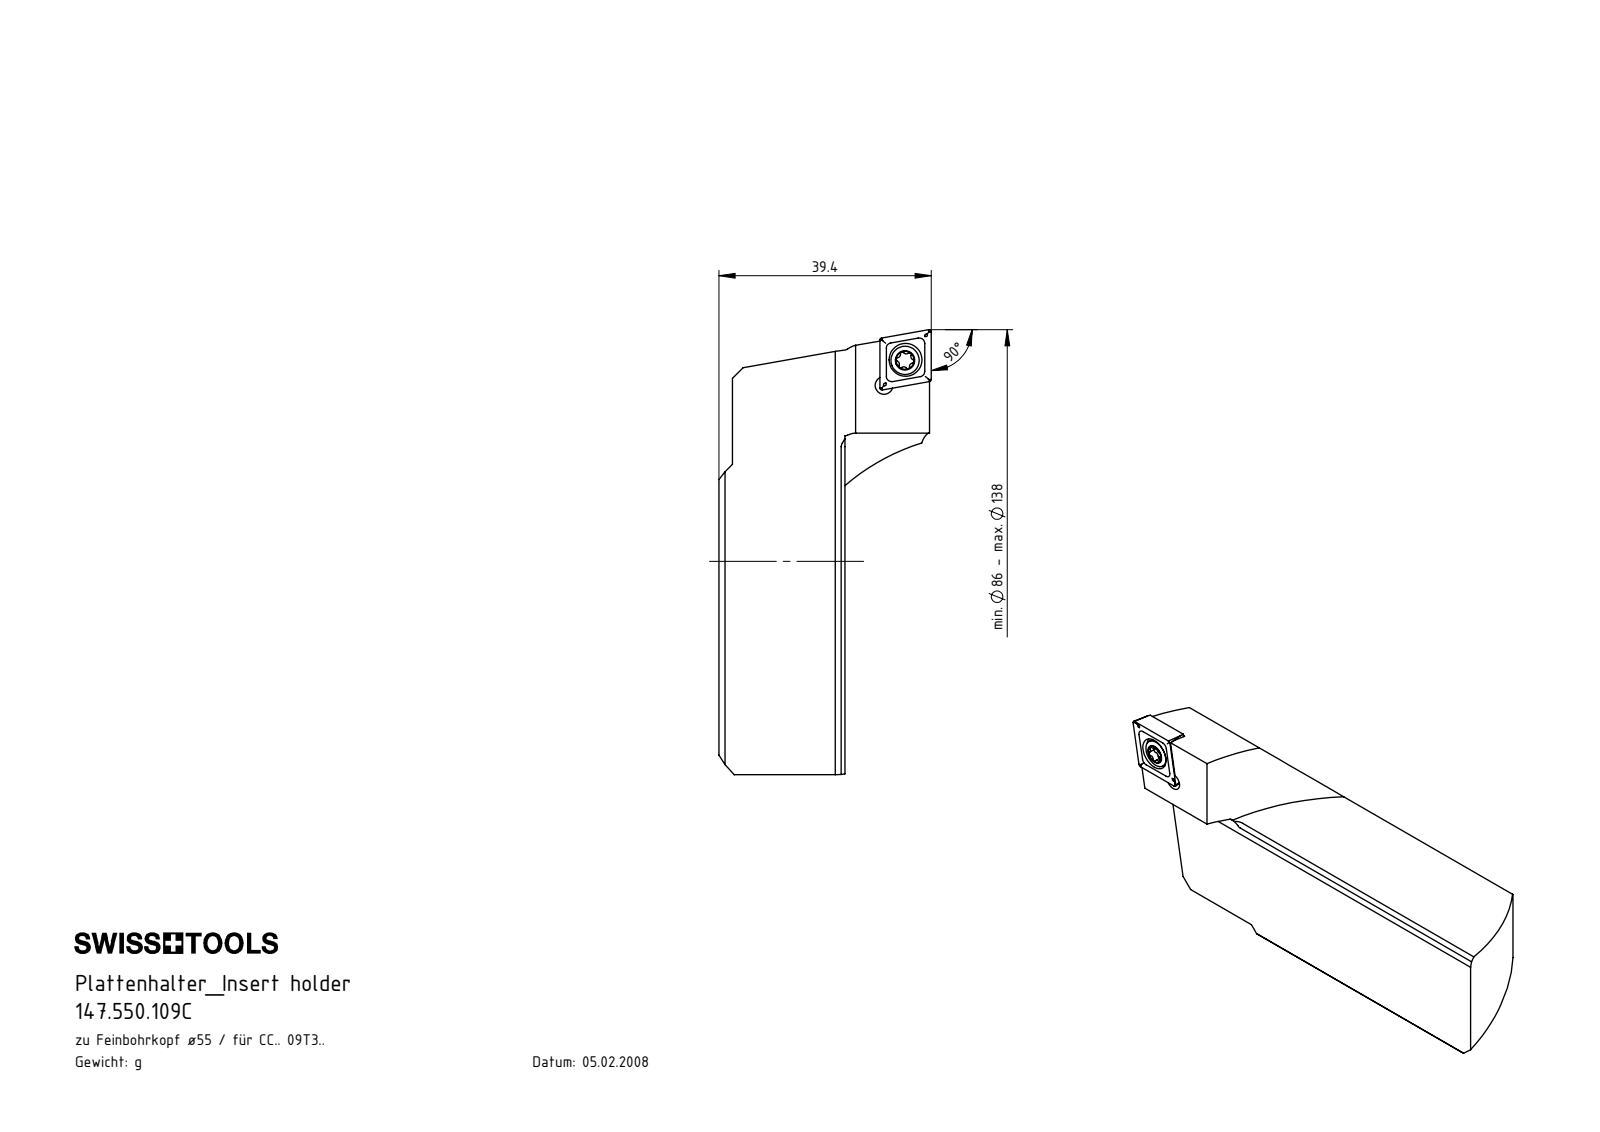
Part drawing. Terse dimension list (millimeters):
name: F00-WCB.086.001_C; WCB-ER2.001.009_A; 147.550.109C; CCMT09T304
written by: SolidWorks 2017 (CONFIG_CONTROL_DESIGN)
unit: mm
bodies: 3 solids, 382 faces (226 planar, 39 cylindrical, 117 other)
size: 82.57 × 39.4 × 27.35
volume: 33 561 mm³; area: 8 976 mm²
holes: 2× ⌀3.3, 1× ⌀4.4, 1× ⌀6.1
bosses: 1× ⌀5.25, 1× ⌀4
rounds: 8× R0.2, 6× R0.34, 6× R0.59, 3× R40, 1× R0.8
face distances: 2.38, 4.76, 21.3, 7.14, 9.52, 4.77, 7.15, 9.53, 11.91, 11.9
hole spacings: 6.07, 6.19
